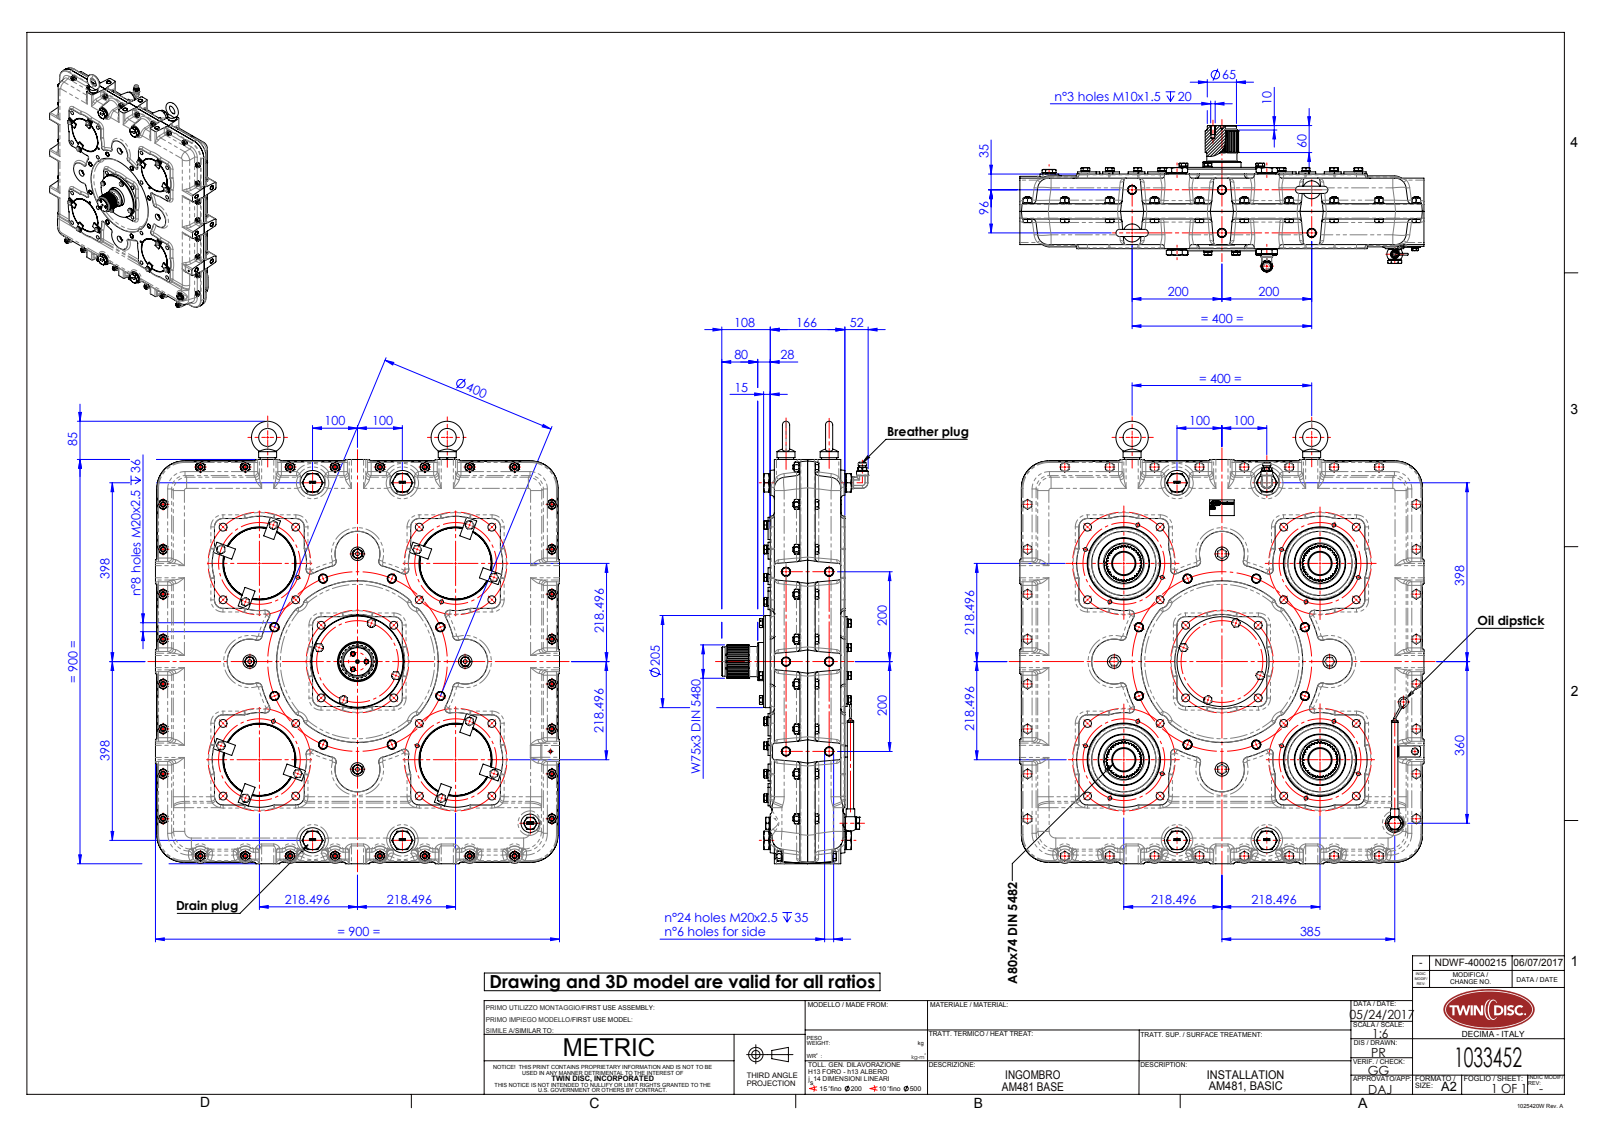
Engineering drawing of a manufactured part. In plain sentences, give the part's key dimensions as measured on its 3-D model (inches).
The part is named "1033452; ITam270-004_rev00-installation; ITam270-003_rev00-installation; IT2021490_rev00-installation (+5 more)". Its 3-D file was written by "SolidWorks 2015 (AUTOMOTIVE_DESIGN)". It is 198 solids with 10140 faces: 3663 planar, 3636 cylindrical and 2841 other. Overall it measures 38.78 by 35.433 by 12.835 inches. Its volume is 6 231 cubic inches and its surface area 9 999 square inches. Round holes: 43 of diameter 0.335, 40 of diameter 0.689, 37 of diameter 0.512, 36 of diameter 0.406, 36 of diameter 0.48, 20 of diameter 0.402, 20 of diameter 0.433, 18 of diameter 0.787, 6 of diameter 0.394, 5 of diameter 3.543, 5 of diameter 5.435, 5 of diameter 5.512. Round bosses or shafts: 36 of diameter 0.831, 36 of diameter 0.709, 36 of diameter 0.472, 21 of diameter 0.394, 20 of diameter 0.713, 20 of diameter 0.638, 6 of diameter 1.575, 5 of diameter 6.295. Partial cylindrical surfaces (rounded edges, fillets, slot ends): 346 of radius 0.014, 288 of radius 1.509, 150 of radius 0.315, 58 of radius 1.163, 48 of radius 0.787, 36 of radius 0.432, 32 of radius 0.197, 32 of radius 0.748. The main face-to-face distances are 2.913, 0.354, 3.268, 6.181, 5.827, 6.535, 0.197, 6.378, 0.157, 6.024. The hole center spacings are 7.874, 3.716, 3.937, 5.744, 8.644, 8.734, 9.713, 11.136.
